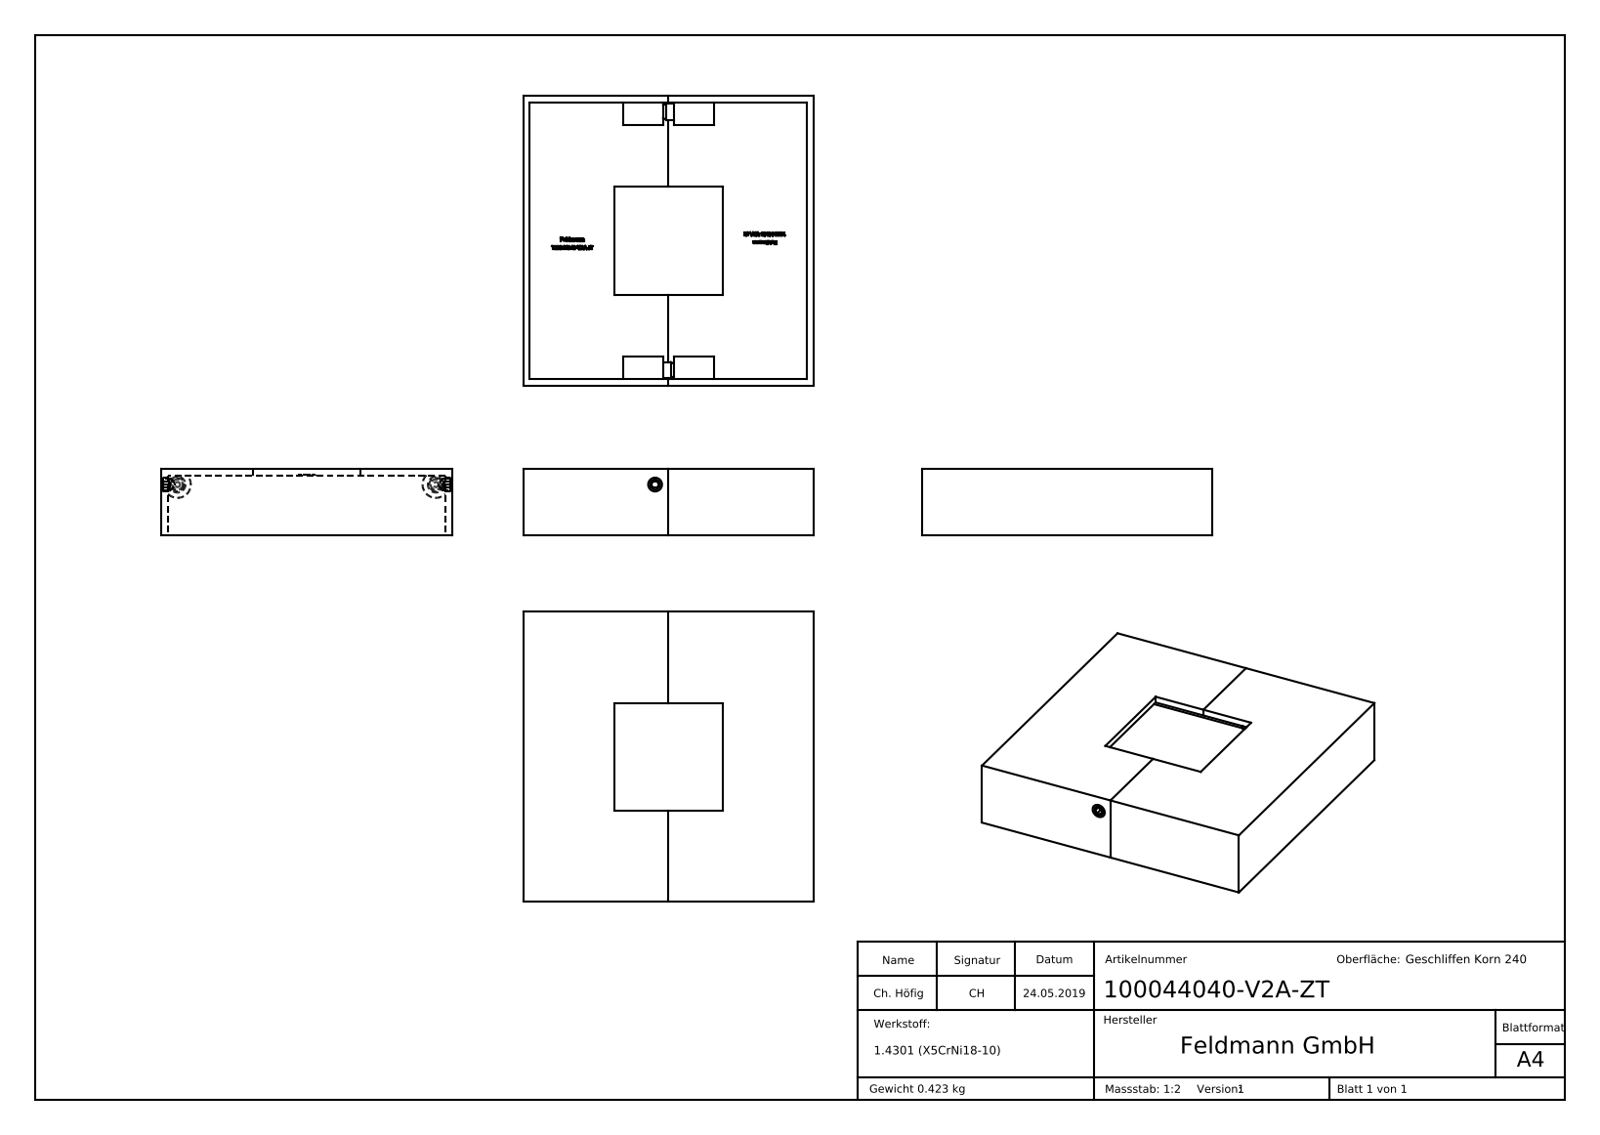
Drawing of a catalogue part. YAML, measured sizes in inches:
part_name: "100044040-V2A-ZT; 100044040-ZT Teil2_100044040-ZT Teil2; DIN914_DIN 914 M5x5; 100044040-ZT Teil1_100044040-V2A-ZT Teil1"
step_written_by: "SolidWorks 2015 (CONFIG_CONTROL_DESIGN)"
units: inches
bodies: {solids: 6, faces: 690, planar: 426, cylindrical: 30, other: 234}
overall_size: [4.291, 4.291, 0.984]
volume: 3.267
surface_area: 68.49
round_holes:
  - {diameter: 0.165, count: 2}
  - {diameter: 0.197, count: 2}
round_bosses_or_shafts:
  - {diameter: 0.236, count: 2}
  - {diameter: 0.197, count: 2}
partial_cylinders:
  - {radius: 0.197, count: 2}
face_to_face_distances: [0.098, 4.193, 4.291, 4.094, 2.146, 2.047, 0.886, 0.984, 1.348, 2.943]
hole_center_spacings: [0.394, 3.819]
